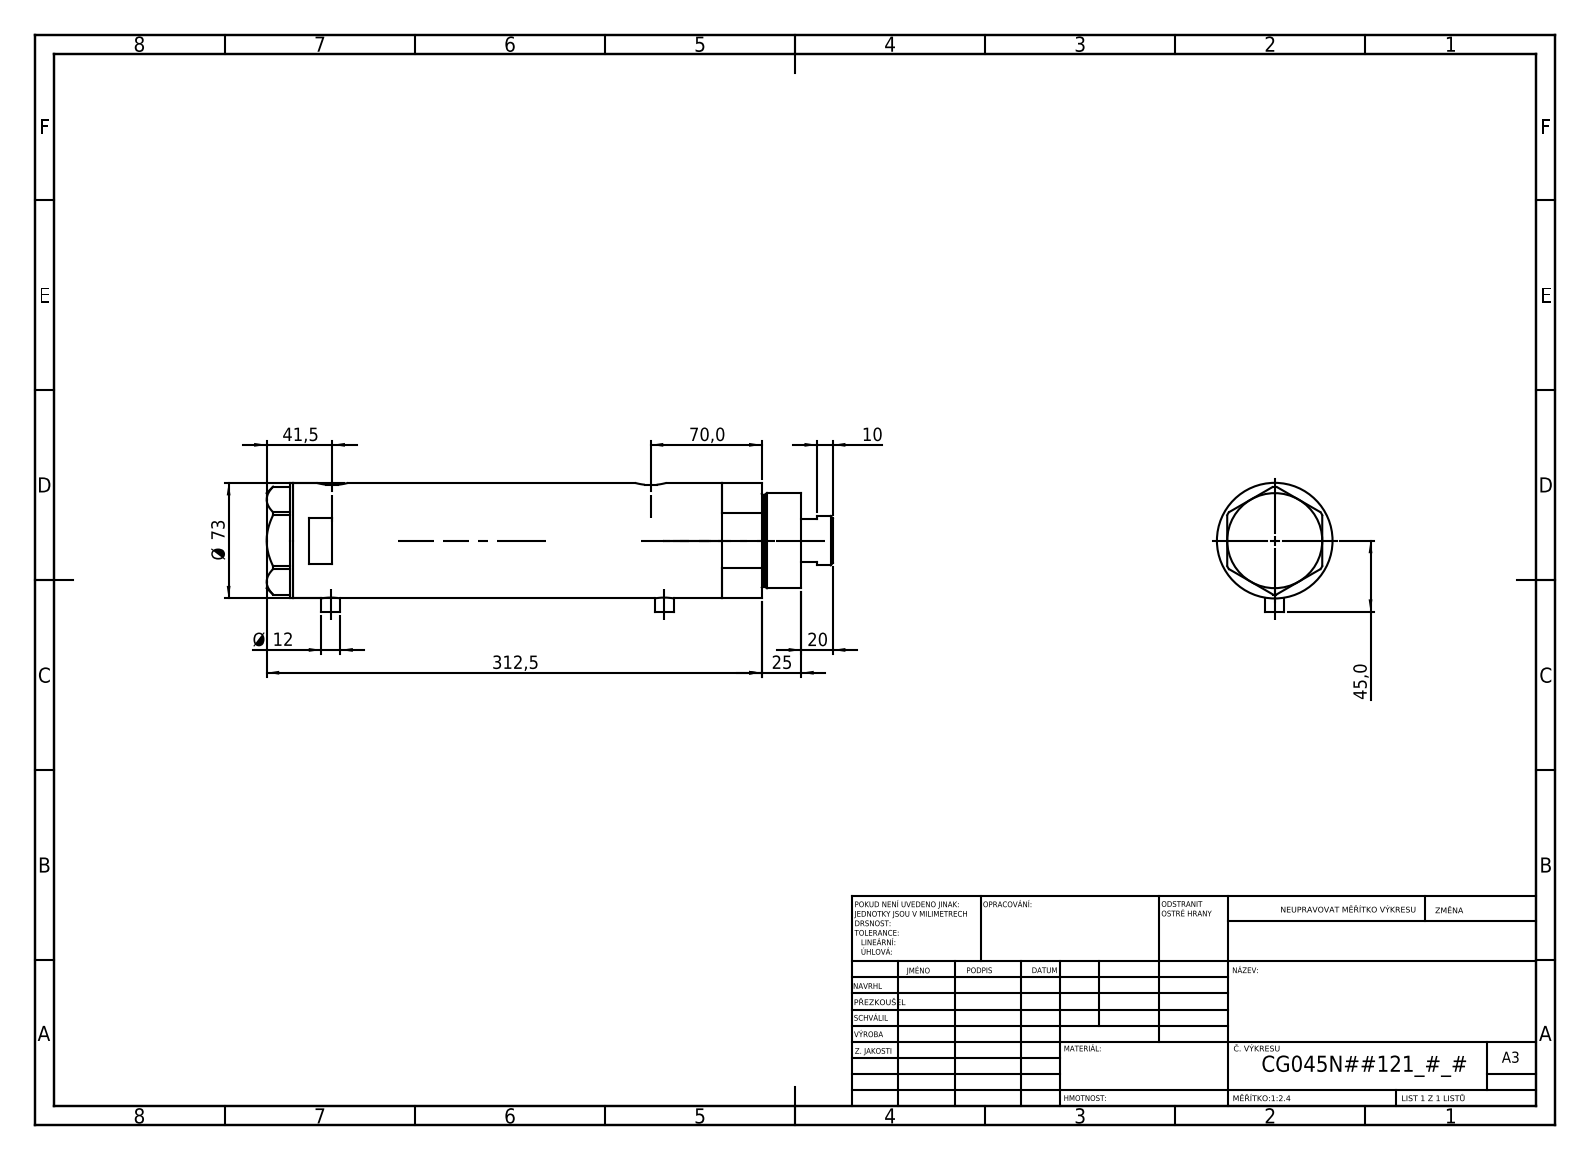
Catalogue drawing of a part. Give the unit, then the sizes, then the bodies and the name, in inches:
Units: inches
Overall size (bounding box): 14.075 × 3.209 × 2.874
Round holes (diameter × count): ⌀0.492 ×2, ⌀0.518 ×2, ⌀0.413 ×1, ⌀1.26 ×1, ⌀1.319 ×1, ⌀1.772 ×1, ⌀1.89 ×1, ⌀2.52 ×1
Round bosses / shafts (diameter × count): ⌀0.472 ×2, ⌀2.874 ×1, ⌀2.362 ×1, ⌀2.283 ×1, ⌀1.22 ×1
Partial cylindrical surfaces — rounded edges, fillets, slot ends (radius × count): R0.394 ×2
Main face-to-face distances: 8.898, 1.024, 7.874, 0.65, 1.673, 9.547, 0.079, 12.638, 3.74, 13.287
Hole centre spacings: 0.039, 0.335, 7.913, 7.953, 8.248, 8.287
Volume: 77.5 in³ · Surface area: 309.7 in²
Bodies: 4 solids, 120 faces (49 planar, 51 cylindrical, 20 other)
Part name (STEP PRODUCT): V270CG_FRONT; V270CG_VC; V270CG_BACK; V270CG_MIDDLE
STEP written by: SolidWorks 2019 (CONFIG_CONTROL_DESIGN)
